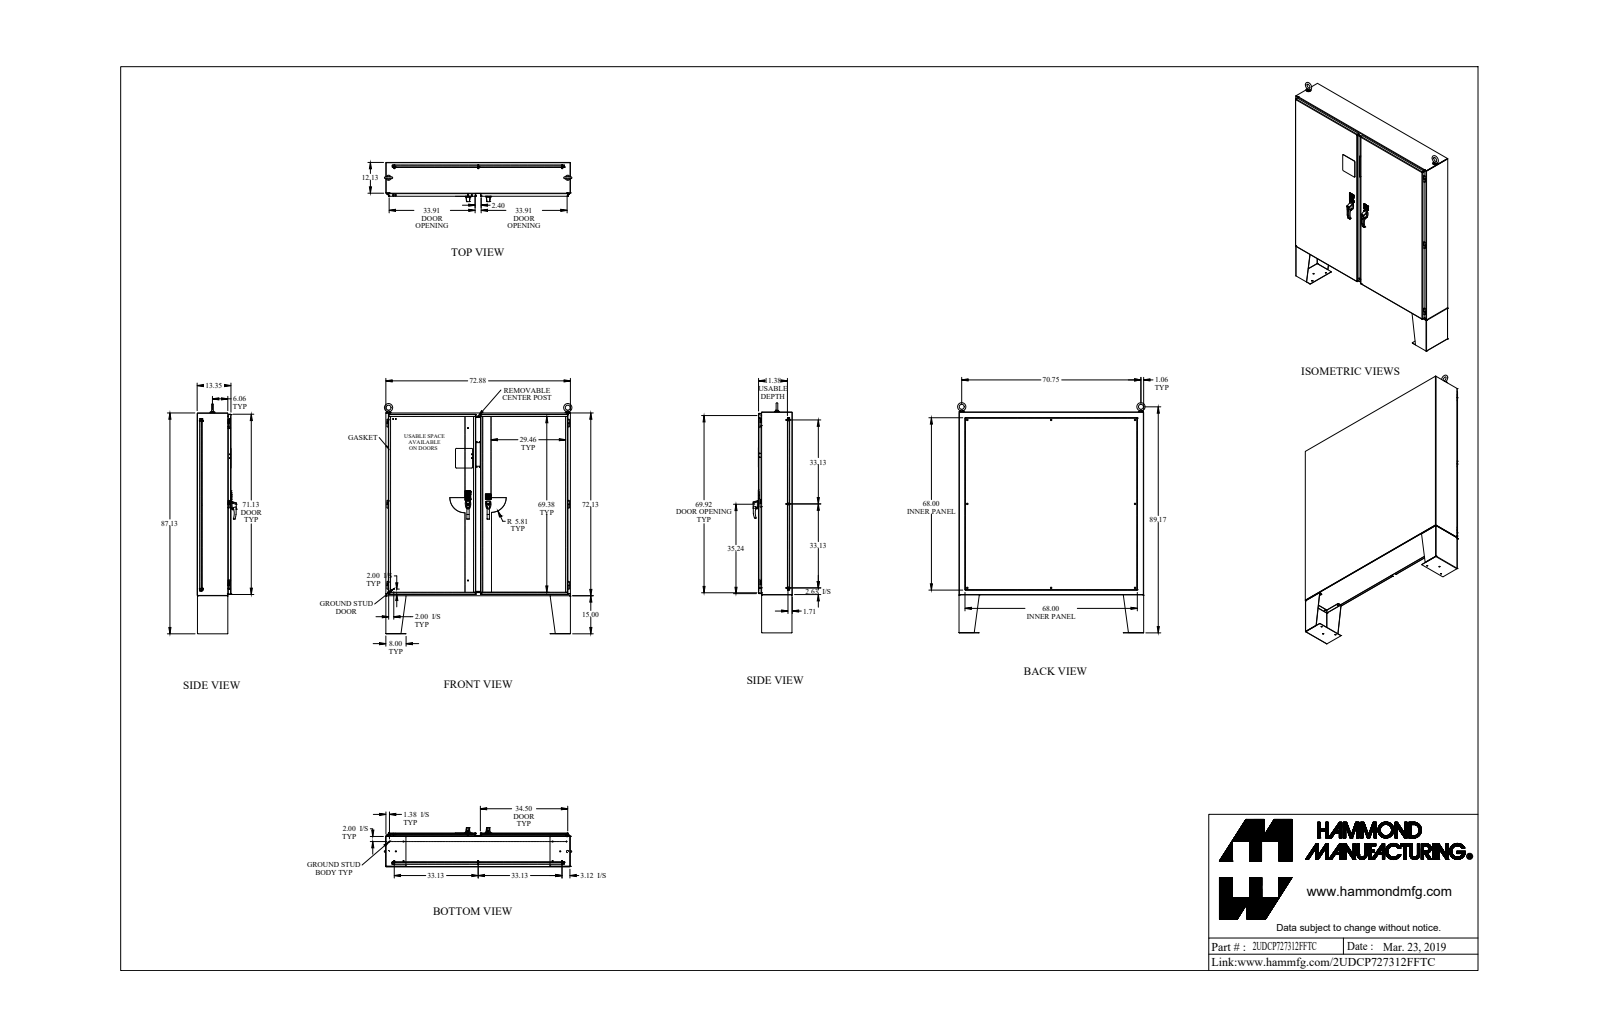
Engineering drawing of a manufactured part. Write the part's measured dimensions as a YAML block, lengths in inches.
part_name: "2UDCP727312FFTC"
step_written_by: "SolidWorks 2018 (AUTOMOTIVE_DESIGN)"
units: inches
bodies: {solids: 178, faces: 2694, planar: 1564, cylindrical: 810, other: 320}
overall_size: [90.799, 73.997, 15.465]
volume: 4629
surface_area: 46965
round_holes:
  - {diameter: 0.437, count: 14}
  - {diameter: 0.307, count: 10}
  - {diameter: 0.281, count: 9}
  - {diameter: 0.25, count: 8}
  - {diameter: 0.35, count: 8}
  - {diameter: 0.313, count: 6}
  - {diameter: 0.196, count: 5}
  - {diameter: 0.445, count: 5}
  - {diameter: 0.257, count: 4}
  - {diameter: 0.28, count: 4}
  - {diameter: 0.39, count: 4}
  - {diameter: 0.413, count: 4}
round_bosses_or_shafts:
  - {diameter: 0.25, count: 14}
  - {diameter: 1, count: 12}
  - {diameter: 0.375, count: 9}
  - {diameter: 0.65, count: 8}
  - {diameter: 0.33, count: 8}
  - {diameter: 0.281, count: 8}
  - {diameter: 0.75, count: 4}
  - {diameter: 0.63, count: 4}
partial_cylinders:
  - {radius: 0.06, count: 54}
  - {radius: 0.125, count: 44}
  - {radius: 0.5, count: 38}
  - {radius: 0.017, count: 32}
  - {radius: 0.185, count: 29}
  - {radius: 0.048, count: 16}
  - {radius: 0.143, count: 16}
  - {radius: 0.03, count: 12}
face_to_face_distances: [0.125, 0.072, 11.431, 13.368, 13.243, 1.937, 1.812, 1.865, 1.741, 11.503]
hole_center_spacings: [7.996, 4.888, 6.228, 8.074, 9.964, 10.99, 61.996, 65.01]
